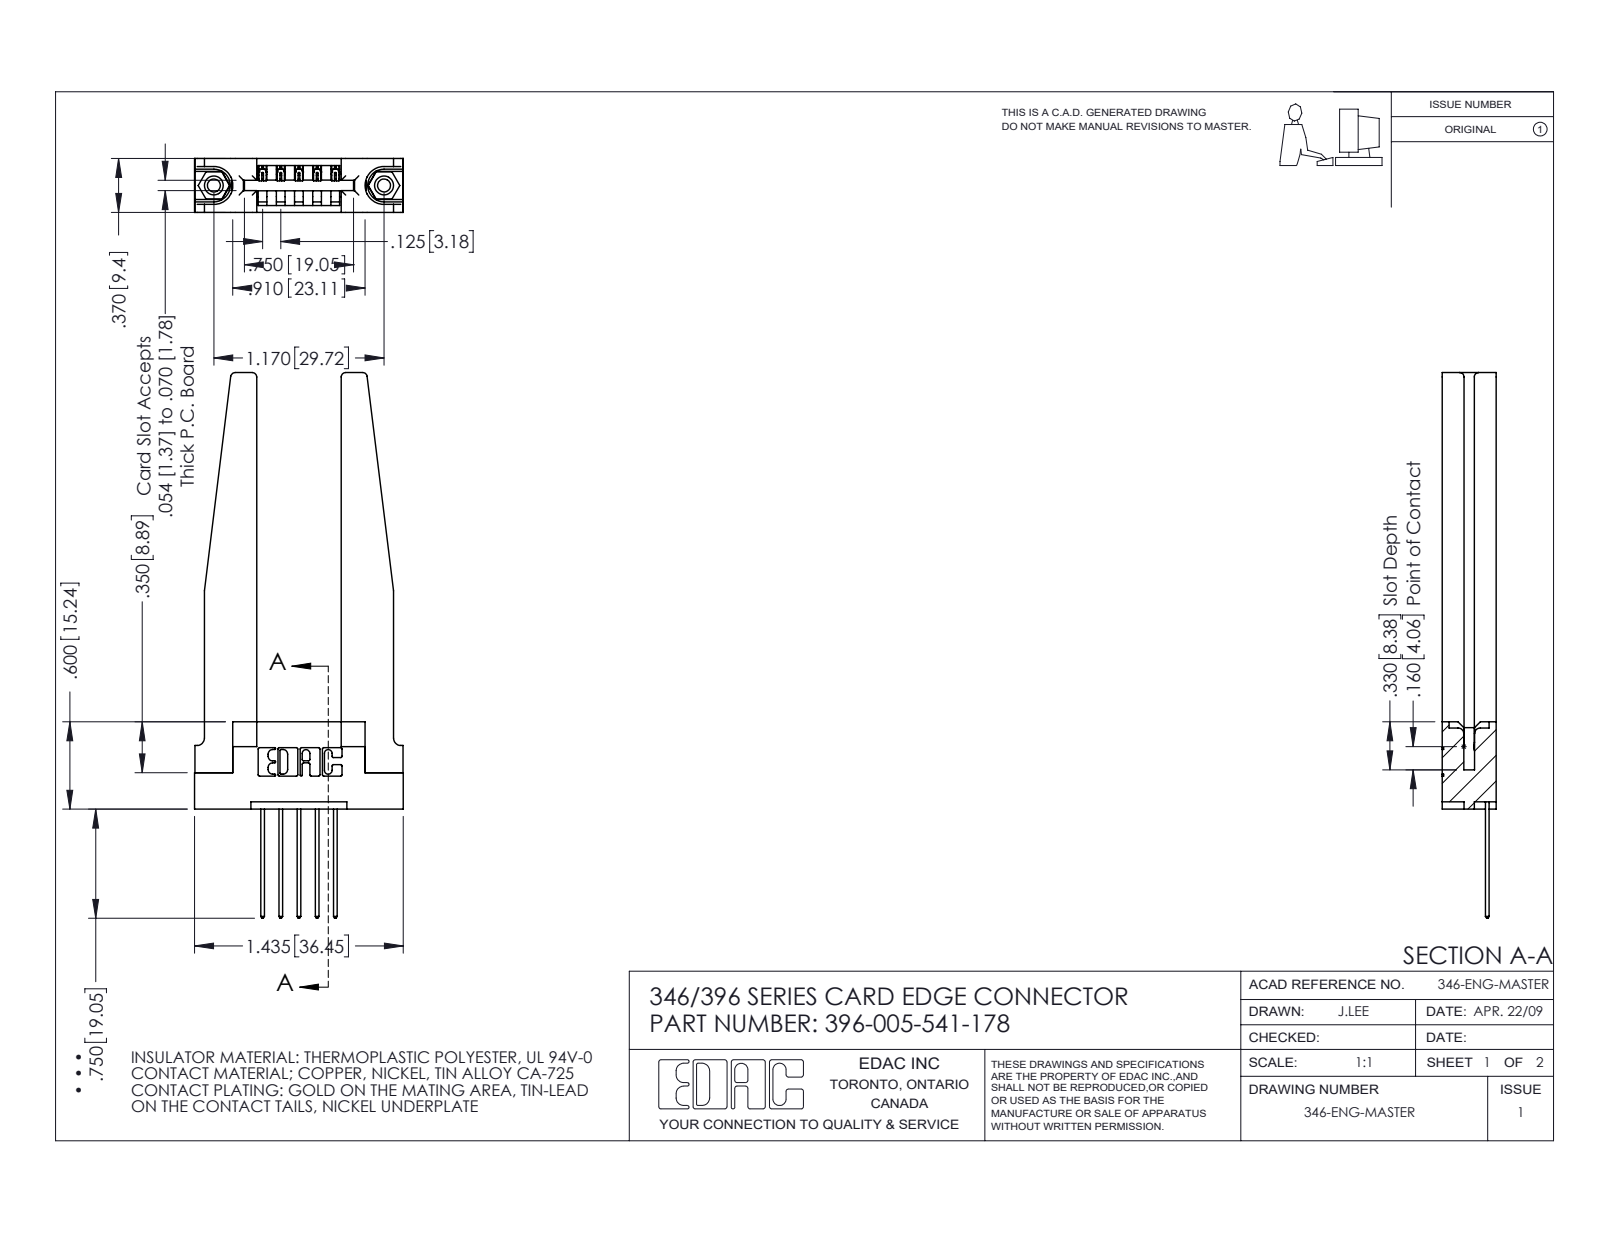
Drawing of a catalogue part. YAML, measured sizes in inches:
part_name: "345-292-001_345-293-141; 346 Part_Flush Mounting Lugs - 0.156 Dia-TH; 346-220-078_345-220-078; 396-005-541-178 (+1 more)"
step_written_by: "SolidWorks 2016 (CONFIG_CONTROL_DESIGN)"
units: inches
bodies: {solids: 10, faces: 646, planar: 418, cylindrical: 176, other: 52}
overall_size: [3.75, 1.435, 0.37]
volume: 0.62
surface_area: 15.97
round_holes:
  - {diameter: 0.089, count: 2}
  - {diameter: 0.125, count: 2}
  - {diameter: 0.156, count: 2}
  - {diameter: 0.064, count: 1}
round_bosses_or_shafts:
  - {diameter: 0.155, count: 2}
partial_cylinders:
  - {radius: 0.01, count: 22}
  - {radius: 0.006, count: 10}
  - {radius: 0.01, count: 10}
  - {radius: 0.03, count: 8}
  - {radius: 0.007, count: 6}
  - {radius: 0.031, count: 6}
  - {radius: 0.026, count: 3}
  - {radius: 0.031, count: 2}
face_to_face_distances: [0.37, 0.15, 0.22, 0.25, 0.581, 0.148, 0.072, 0.102, 0.048, 0.322]
hole_center_spacings: [0.246, 0.969, 1.17]
